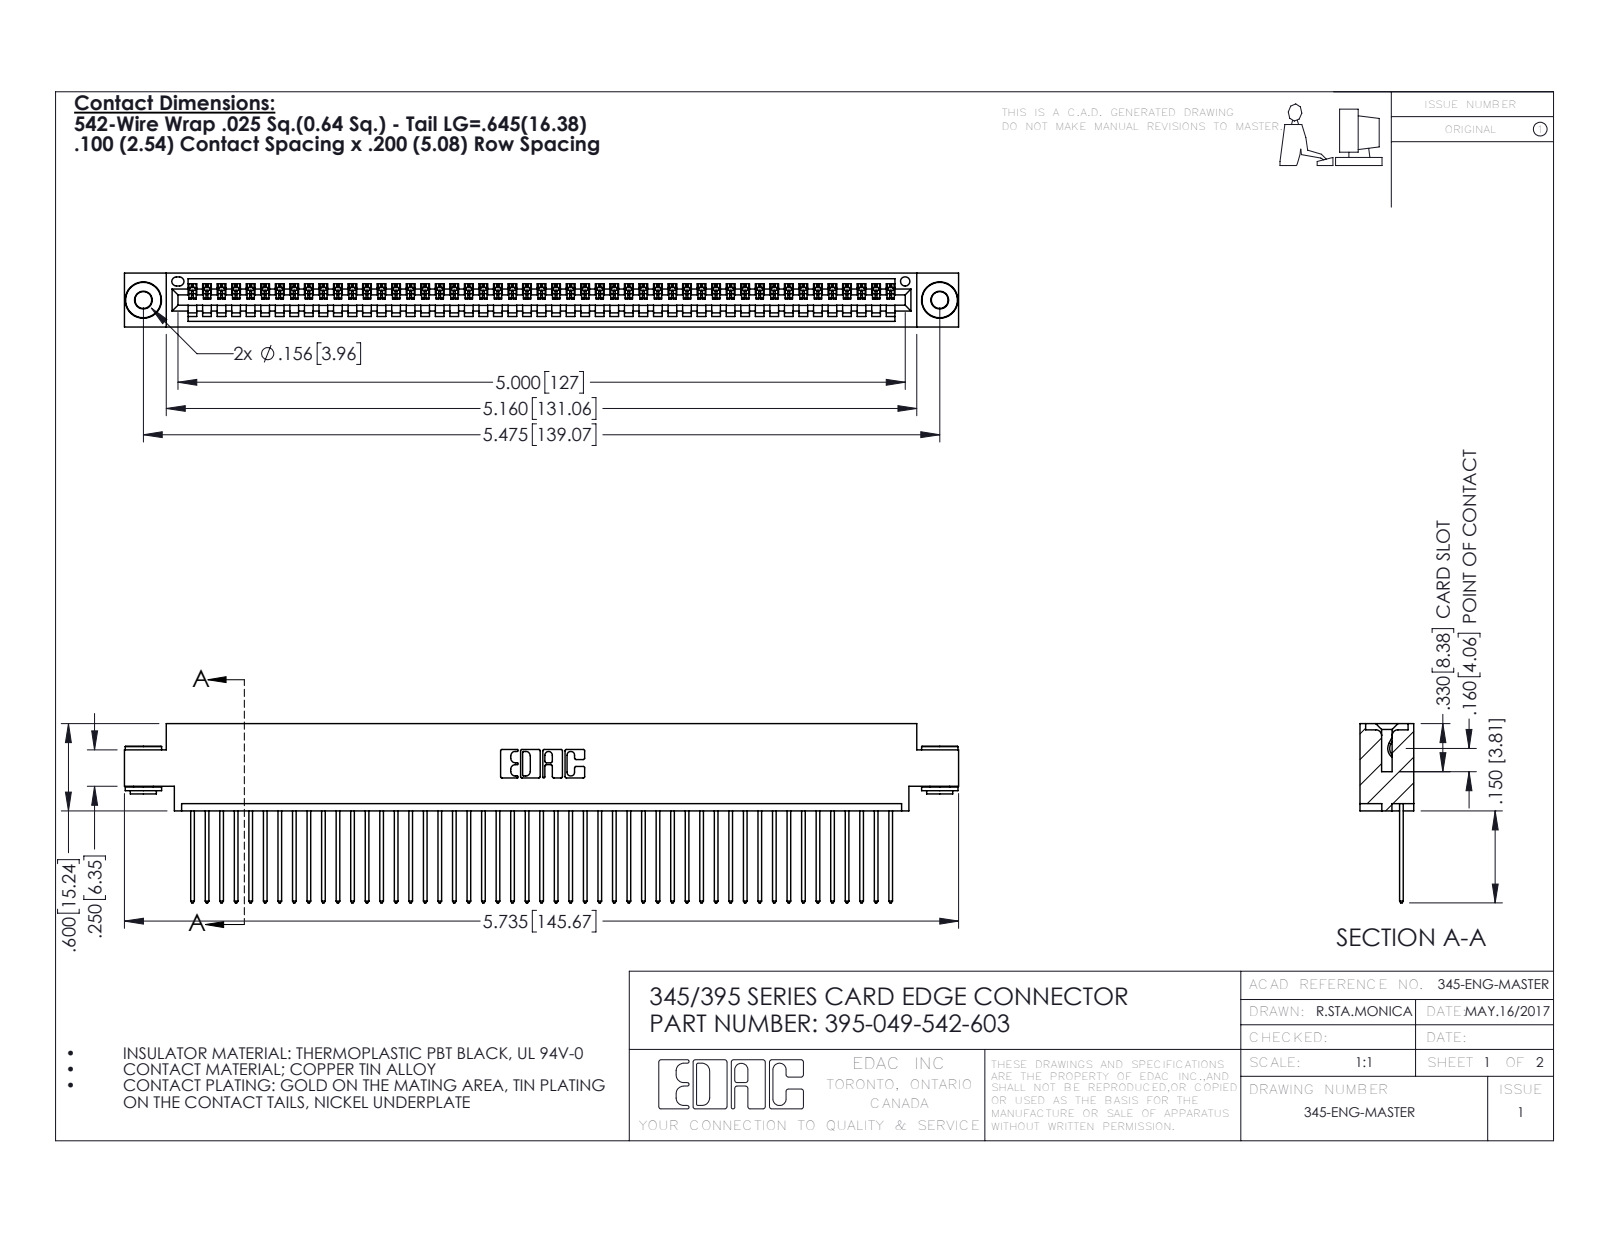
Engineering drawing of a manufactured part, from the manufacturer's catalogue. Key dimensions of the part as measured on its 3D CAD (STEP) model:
Part name (STEP PRODUCT): 345 Part_0.170 Offset - 0.156 Dia-TH; 345-292-001_345-293-142; 395-049-542-603; 345-250-002_345-250-002-102
STEP written by: SolidWorks 2016 (CONFIG_CONTROL_DESIGN)
Units: inches
Bodies: 52 solids, 3010 faces (2054 planar, 948 cylindrical, 8 other)
Overall size (bounding box): 5.735 × 1.232 × 0.37
Volume: 0.849 in³ · Surface area: 30.39 in²
Round holes (diameter × count): ⌀0.116 ×2, ⌀0.156 ×2, ⌀0.064 ×1
Round bosses / shafts (diameter × count): ⌀0.25 ×2, ⌀0.18 ×2, ⌀0.136 ×2
Partial cylindrical surfaces — rounded edges, fillets, slot ends (radius × count): R0.006 ×98, R0.01 ×98, R0.01 ×22, R0.007 ×6, R0.031 ×6, R0.026 ×3, R0.031 ×2, R0.04 ×2
Main face-to-face distances: 0.072, 0.298, 0.37, 0.098, 0.272, 0.025, 0.2, 0.225, 0.175, 0.149
Hole centre spacings: 0.27, 5.239, 5.475
